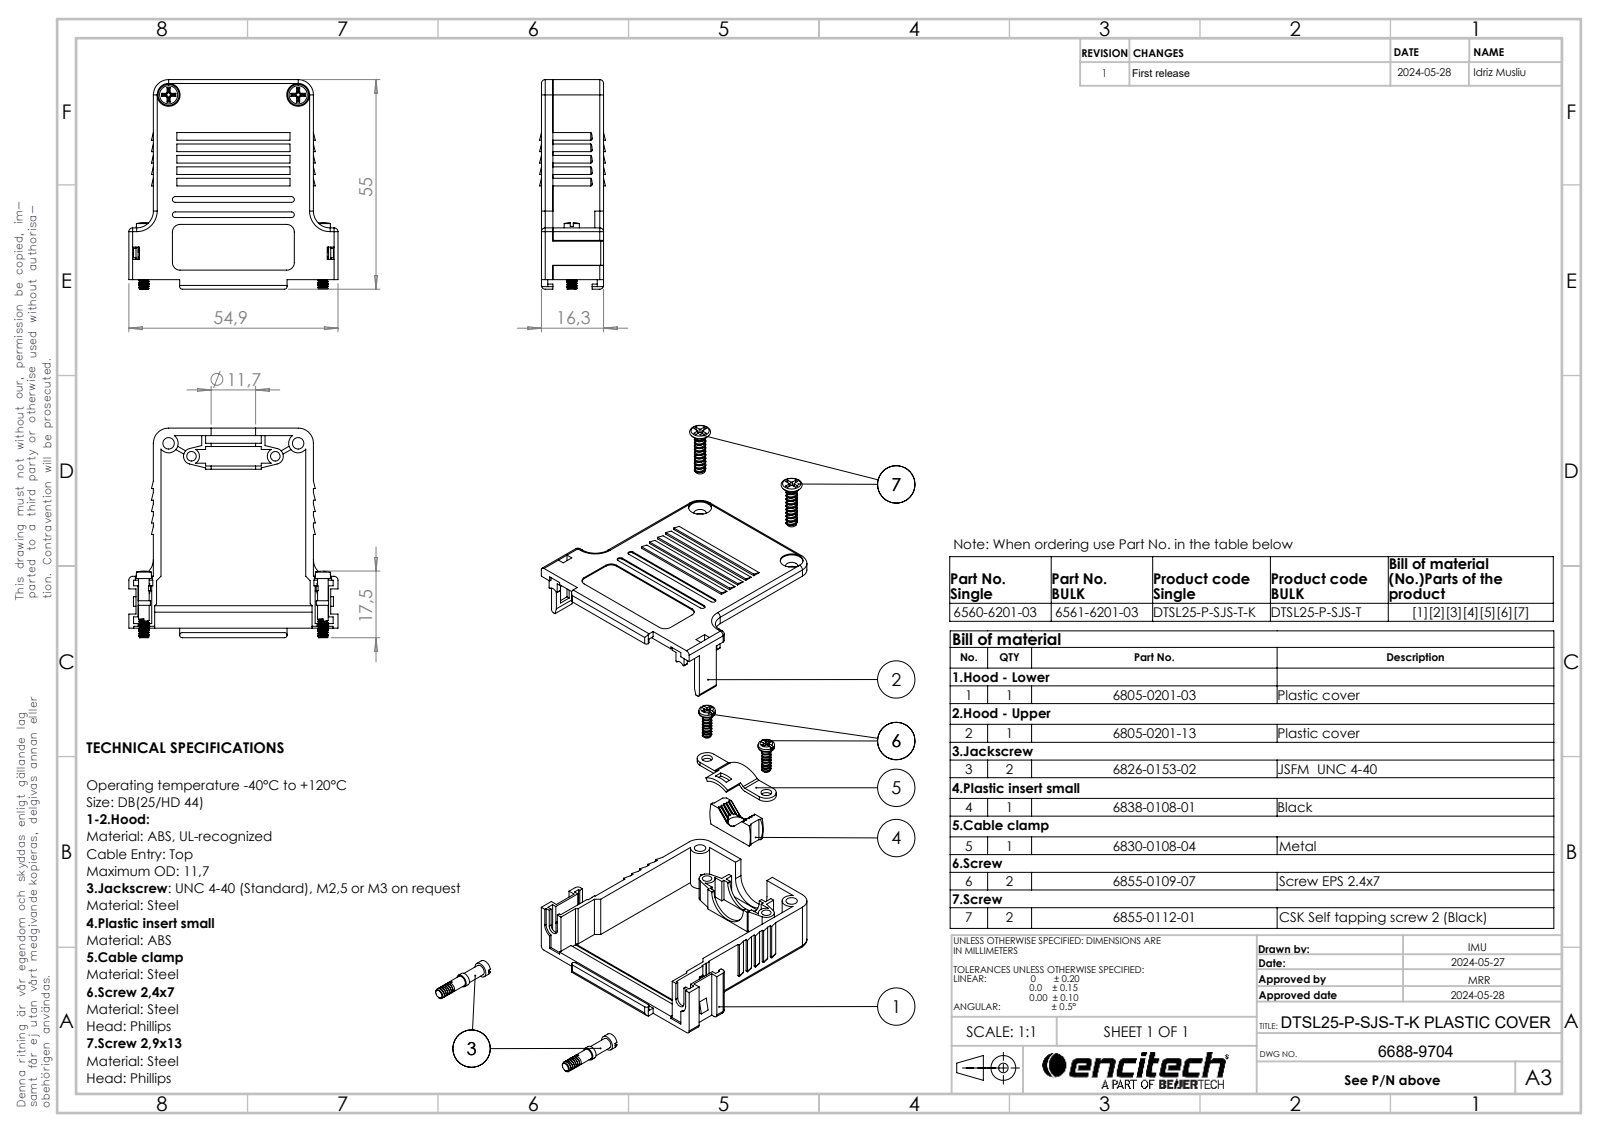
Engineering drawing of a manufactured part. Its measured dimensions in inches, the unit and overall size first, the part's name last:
Units: inches
Overall size (bounding box): 2.165 × 2.161 × 0.681
Round holes (diameter × count): ⌀0.098 ×2, ⌀0.11 ×2, ⌀0.118 ×2, ⌀0.126 ×2, ⌀0.236 ×2, ⌀0.181 ×1
Round bosses / shafts (diameter × count): ⌀0.169 ×2, ⌀0.157 ×2, ⌀0.136 ×2, ⌀0.11 ×2, ⌀0.097 ×2, ⌀0.08 ×2
Partial cylindrical surfaces — rounded edges, fillets, slot ends (radius × count): R0.039 ×18, R0.014 ×15, R0.008 ×8, R0.079 ×7, R0.03 ×6, R0.059 ×4, R0.027 ×2, R0.083 ×2
Main face-to-face distances: 0.079, 0.563, 0.484, 0.642, 0.551, 0.067, 0.039, 0.118, 0.63, 0.445
Hole centre spacings: 0.272, 1.111, 0.433, 0.433, 0.683, 0.683, 0.866, 1.339
Volume: 0.909 in³ · Surface area: 29.49 in²
Bodies: 10 solids, 843 faces (489 planar, 272 cylindrical, 82 other)
Part name (STEP PRODUCT): 6826-0153-02; 6805-0201-03; 6688-9704; 6855-0109-07 (+4 more)
STEP written by: SolidWorks 2021 (AUTOMOTIVE_DESIGN)
